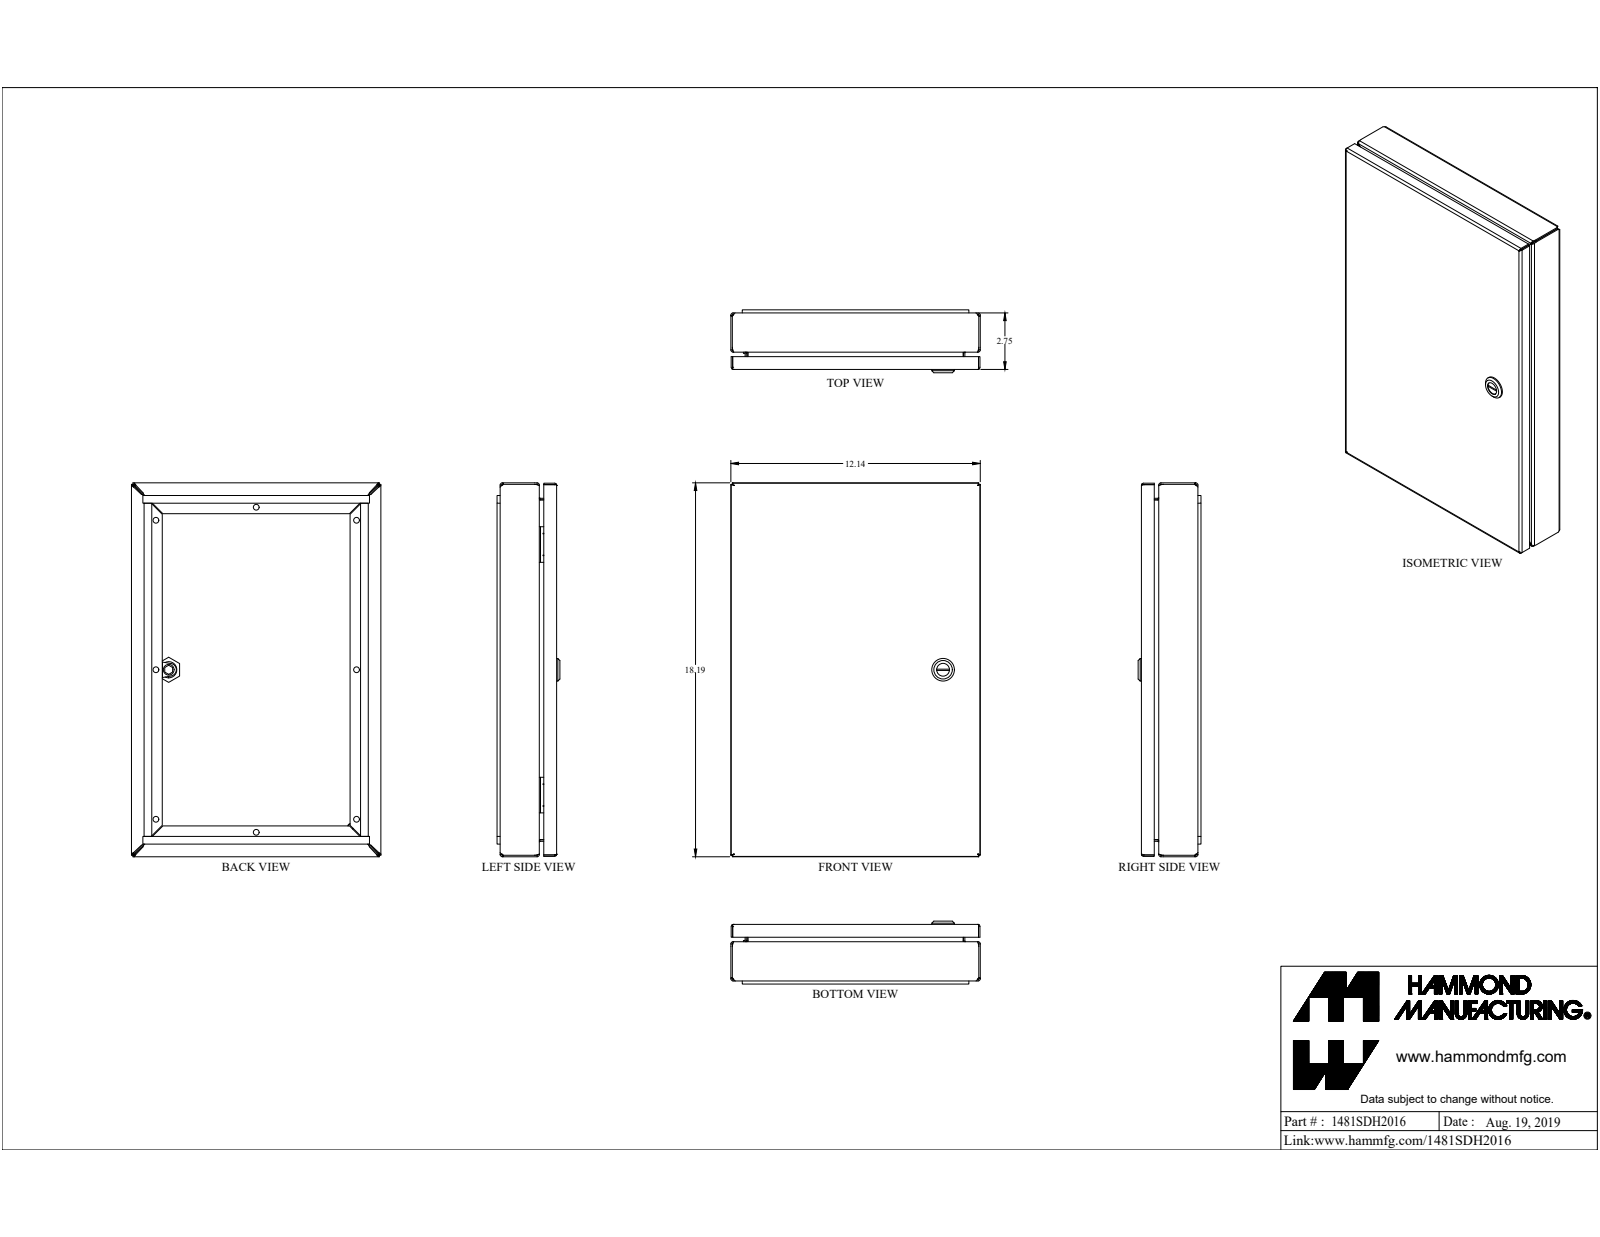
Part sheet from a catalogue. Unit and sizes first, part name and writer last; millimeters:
Units: millimetres
Overall size (bounding box): 462 × 308.4 × 77.7
Round holes (diameter × count): ⌀7.1 ×8, ⌀4.4 ×1, ⌀5.9 ×1, ⌀6.1 ×1, ⌀6.1 ×1, ⌀15.9 ×1, ⌀19.9 ×1
Round bosses / shafts (diameter × count): ⌀27.9 ×1, ⌀13.3 ×1, ⌀11.6 ×1, ⌀10.1 ×1, ⌀9 ×1, ⌀8 ×1, ⌀7.4 ×1, ⌀6.4 ×1
Partial cylindrical surfaces — rounded edges, fillets, slot ends (radius × count): R0.9 ×28, R2.7 ×28, R9.7 ×12, R482.7 ×8, R0.2 ×4, R1.6 ×4, R6.4 ×4, R12.7 ×4
Main face-to-face distances: 1.8, 65.5, 21.4, 44.1, 67.3, 306.5, 63.7, 68, 46.6, 2.5
Hole centre spacings: 125, 405, 248, 184.7, 184.7, 236, 236, 309.2
Volume: 804 100 mm³ · Surface area: 822 600 mm²
Bodies: 23 solids, 614 faces (348 planar, 168 cylindrical, 98 other)
Part name (STEP PRODUCT): 1481SDH2016
STEP written by: SolidWorks 2019 (CONFIG_CONTROL_DESIGN)
